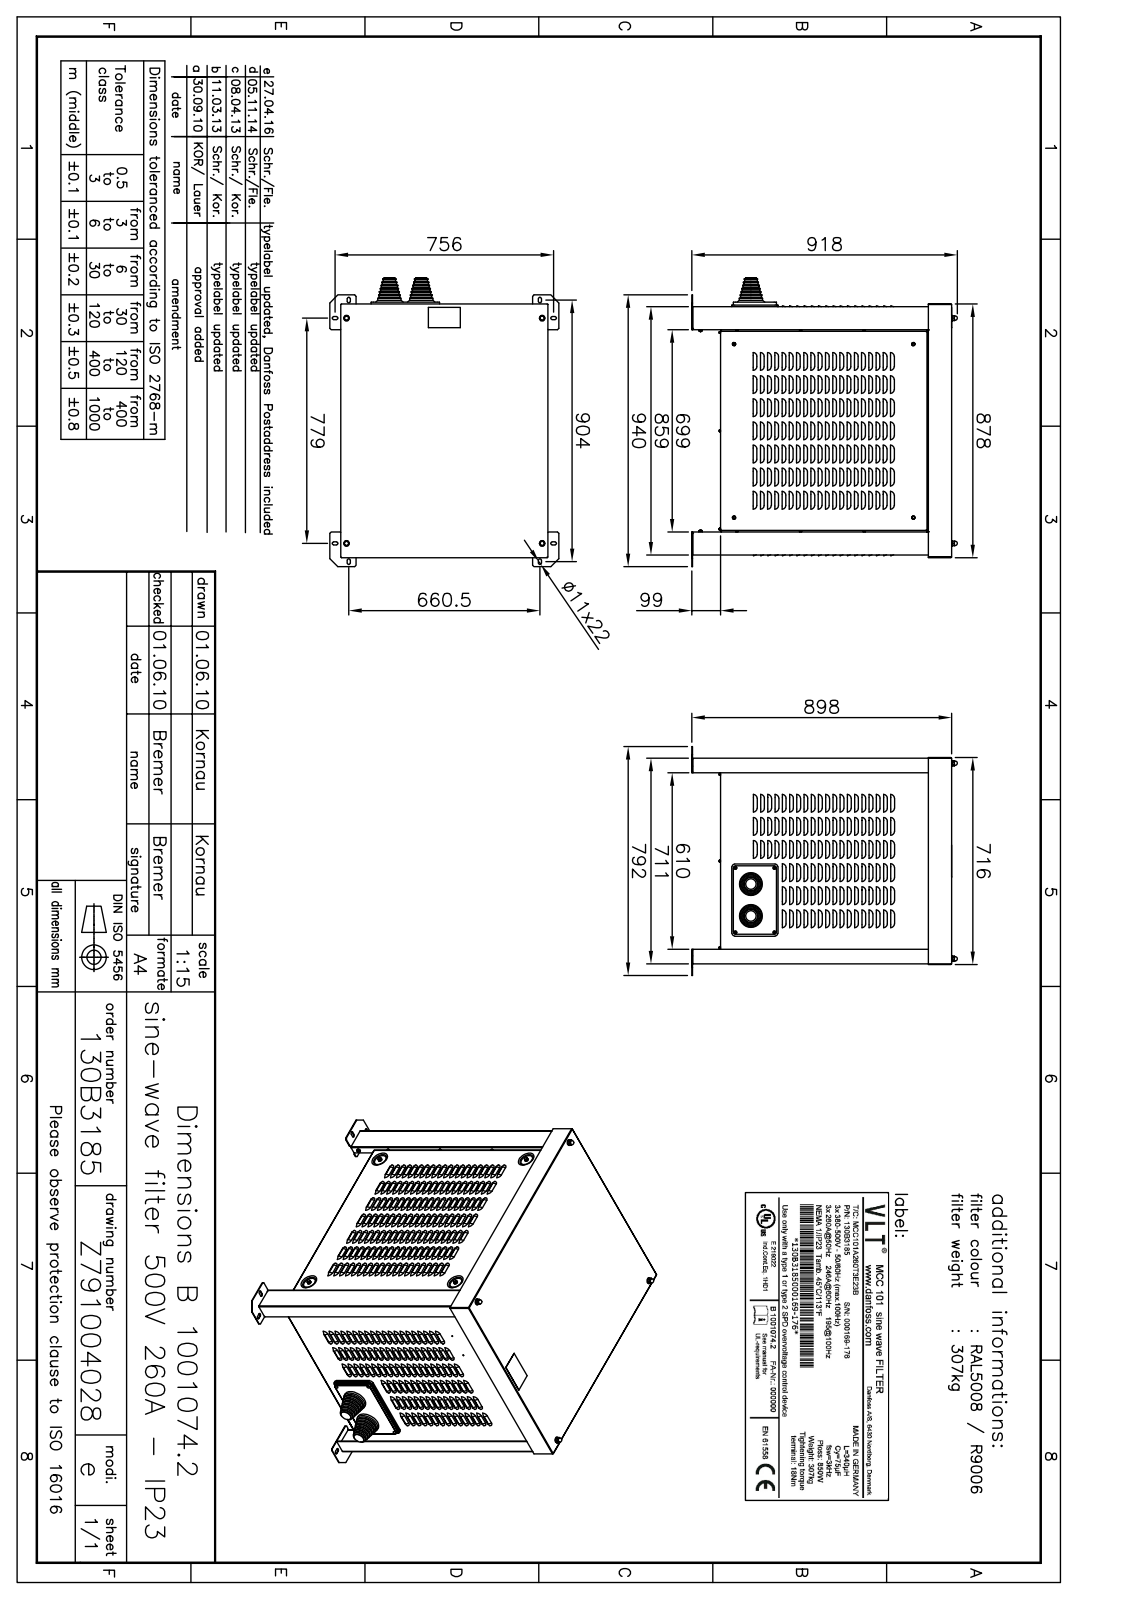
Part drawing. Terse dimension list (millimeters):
name: Kern für B 1001074; #020-1413; Baugruppe #020-2034; #020-1410 (+8 more)
written by: SolidWorks 2014 (AUTOMOTIVE_DESIGN)
unit: mm
bodies: 171 solids, 11413 faces (6021 planar, 2580 cylindrical, 2812 other)
size: 999.5 × 914.6 × 791
volume: 47 860 000 mm³; area: 16 690 000 mm²
holes: 33× ⌀13, 25× ⌀5.5, 20× ⌀11, 16× ⌀8.5, 13× ⌀10.5, 12× ⌀4.2, 10× ⌀10, 9× ⌀6.5, 9× ⌀7.1, 8× ⌀3.3, 8× ⌀3.8, 7× ⌀8
bosses: 19× ⌀12, 18× ⌀6, 10× ⌀20, 6× ⌀65, 6× ⌀20.5, 5× ⌀23, 5× ⌀14.4, 4× ⌀16
rounds: 484× R5, 80× R12, 60× R14, 58× R0.1, 42× R2.1, 24× R0.8, 23× R4, 20× R5.5
face distances: 2, 3, 671, 19, 852, 21, 673, 652, 789.5, 791.5
hole spacings: 340, 680, 0.5, 250, 453.1, 453.43, 689.2, 300
